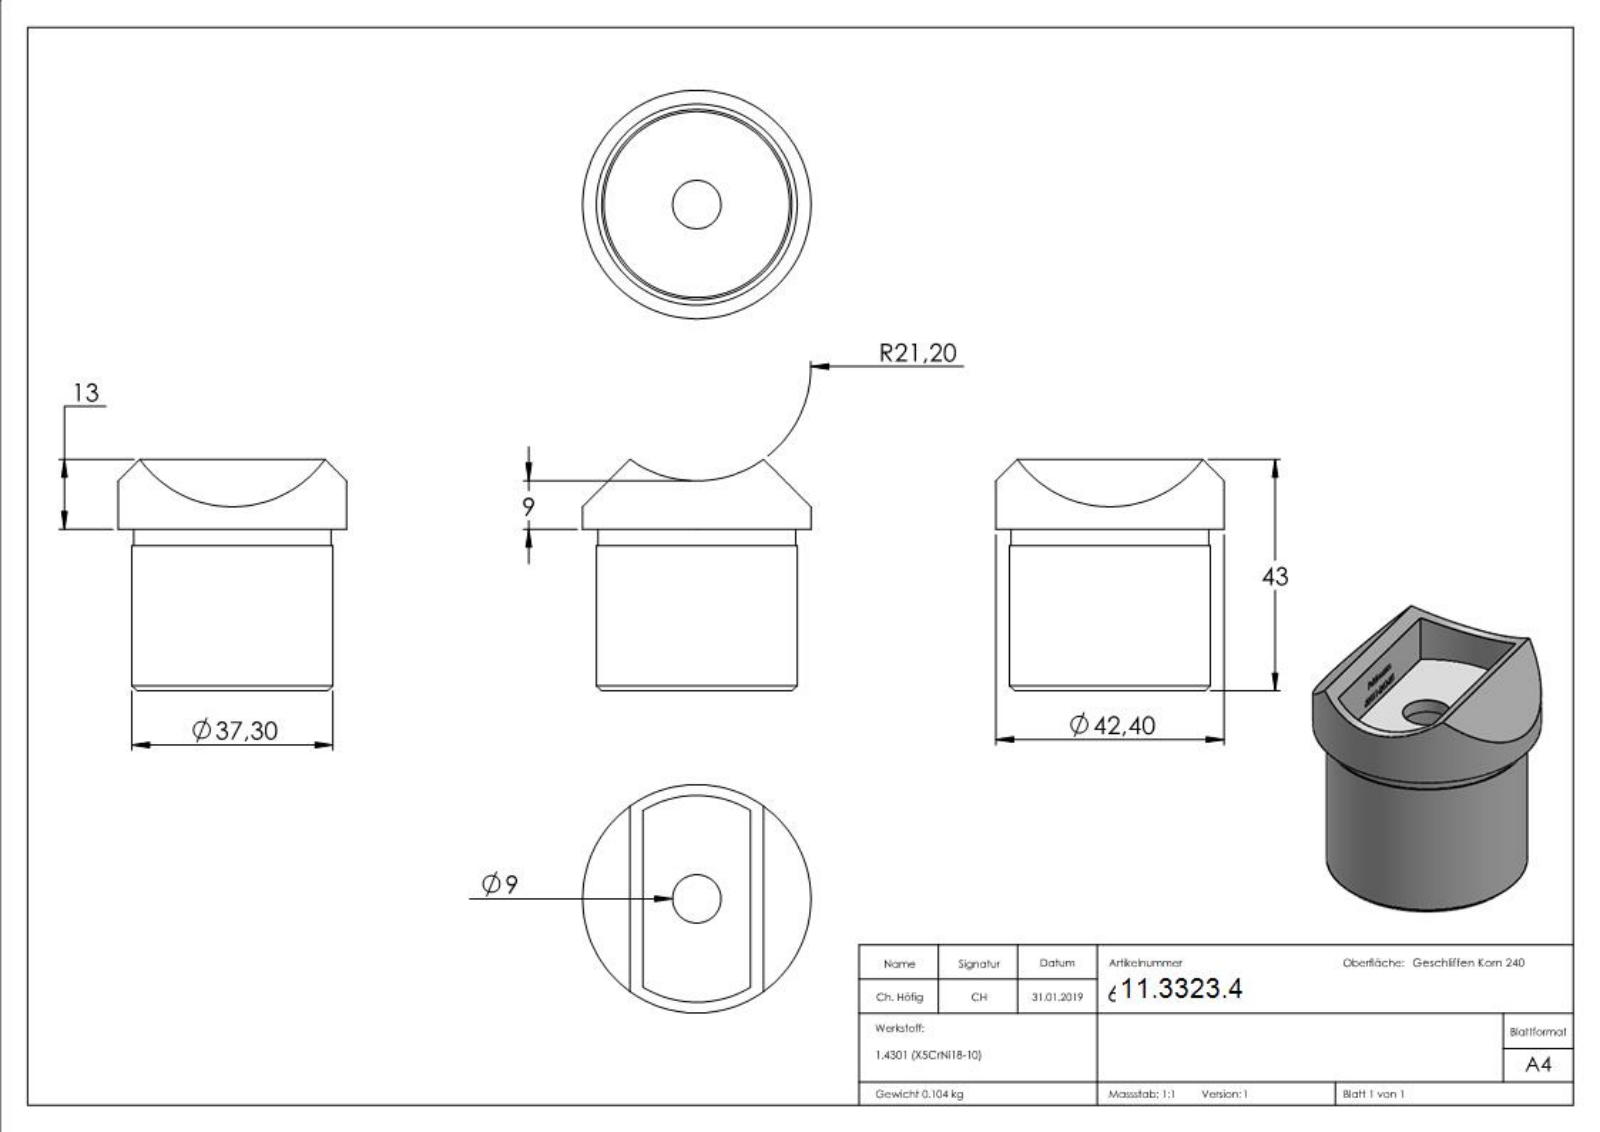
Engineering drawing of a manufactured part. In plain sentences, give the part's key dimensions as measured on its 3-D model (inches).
The part is named "60211-240-25". Its 3-D file was written by "SolidWorks 2018 (CONFIG_CONTROL_DESIGN)". It is 1 solid with 260 faces: 150 planar, 8 cylindrical and 102 other. Overall it measures 1.693 by 1.669 by 1.669 inches. Its volume is 0.803 cubic inches and its surface area 18.25 square inches. Round holes: 1 of diameter 0.354, 1 of diameter 1.358. Round bosses or shafts: 1 of diameter 1.669, 1 of diameter 1.469, 1 of diameter 1.445. Partial cylindrical surfaces (rounded edges, fillets, slot ends): 1 of radius 0.756, 1 of radius 0.835. The main face-to-face distances are 0.098, 0.787, 1.181, 1.28, 1.063, 0.118, 0.217, 0.791, 0.051, 0.04.
